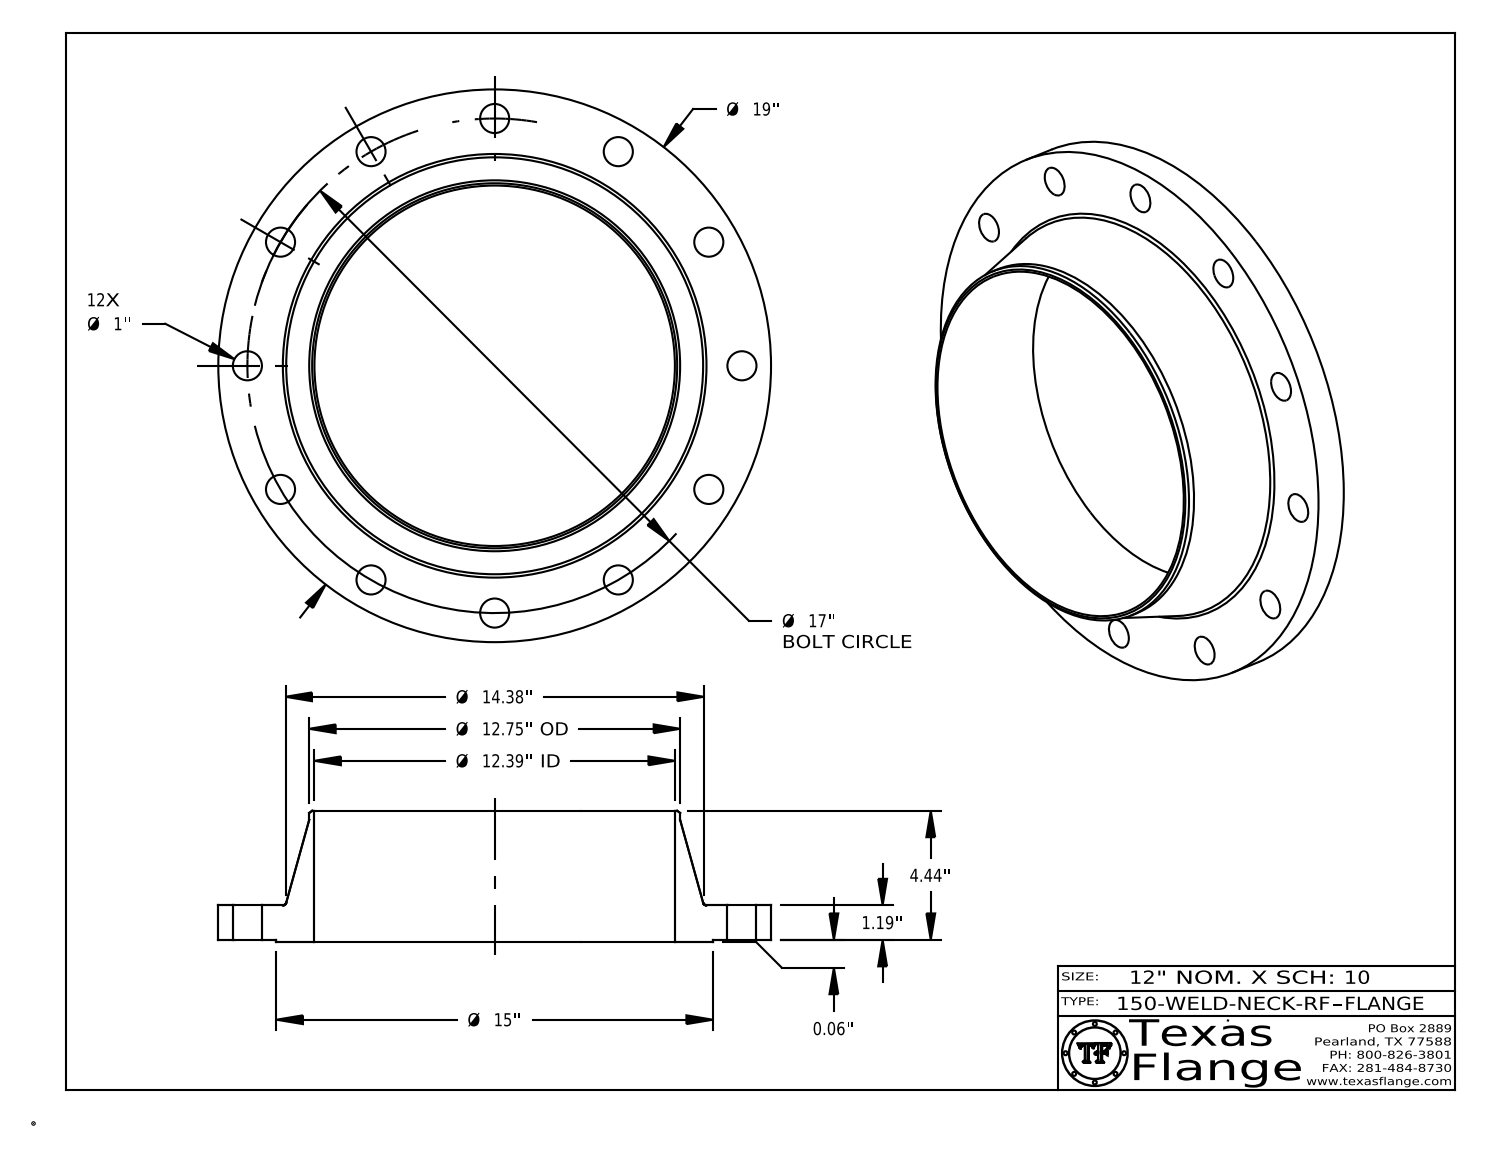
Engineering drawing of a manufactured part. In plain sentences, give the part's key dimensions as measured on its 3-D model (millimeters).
The part is named "150-WELD-NECK-RF". Its 3-D file was written by "CATIA V5 STEP AP214 (AUTOMOTIVE_DESIGN)". It is 1 solid with 427 faces: 369 planar, 52 cylindrical and 6 other. Overall it measures 482.6 by 482.6 by 114.4 millimeters. Its volume is 4 248 000 cubic millimeters and its surface area 455 300 square millimeters. Round holes: 12 of diameter 25.4, 1 of diameter 12.6, 1 of diameter 314.7. Round bosses or shafts: 8 of diameter 0.8, 1 of diameter 482.6, 1 of diameter 381, 1 of diameter 323.9, 1 of diameter 9.9. The main face-to-face distances are 30.2, 1.6, 31.8, 114.4, 112.8, 82.6, 0.4, 31.4, 29.8, 82.9. The hole center spacings are 215.9, 417.1, 111.8, 305.3, 373.9, 111.8, 305.3, 373.9.
